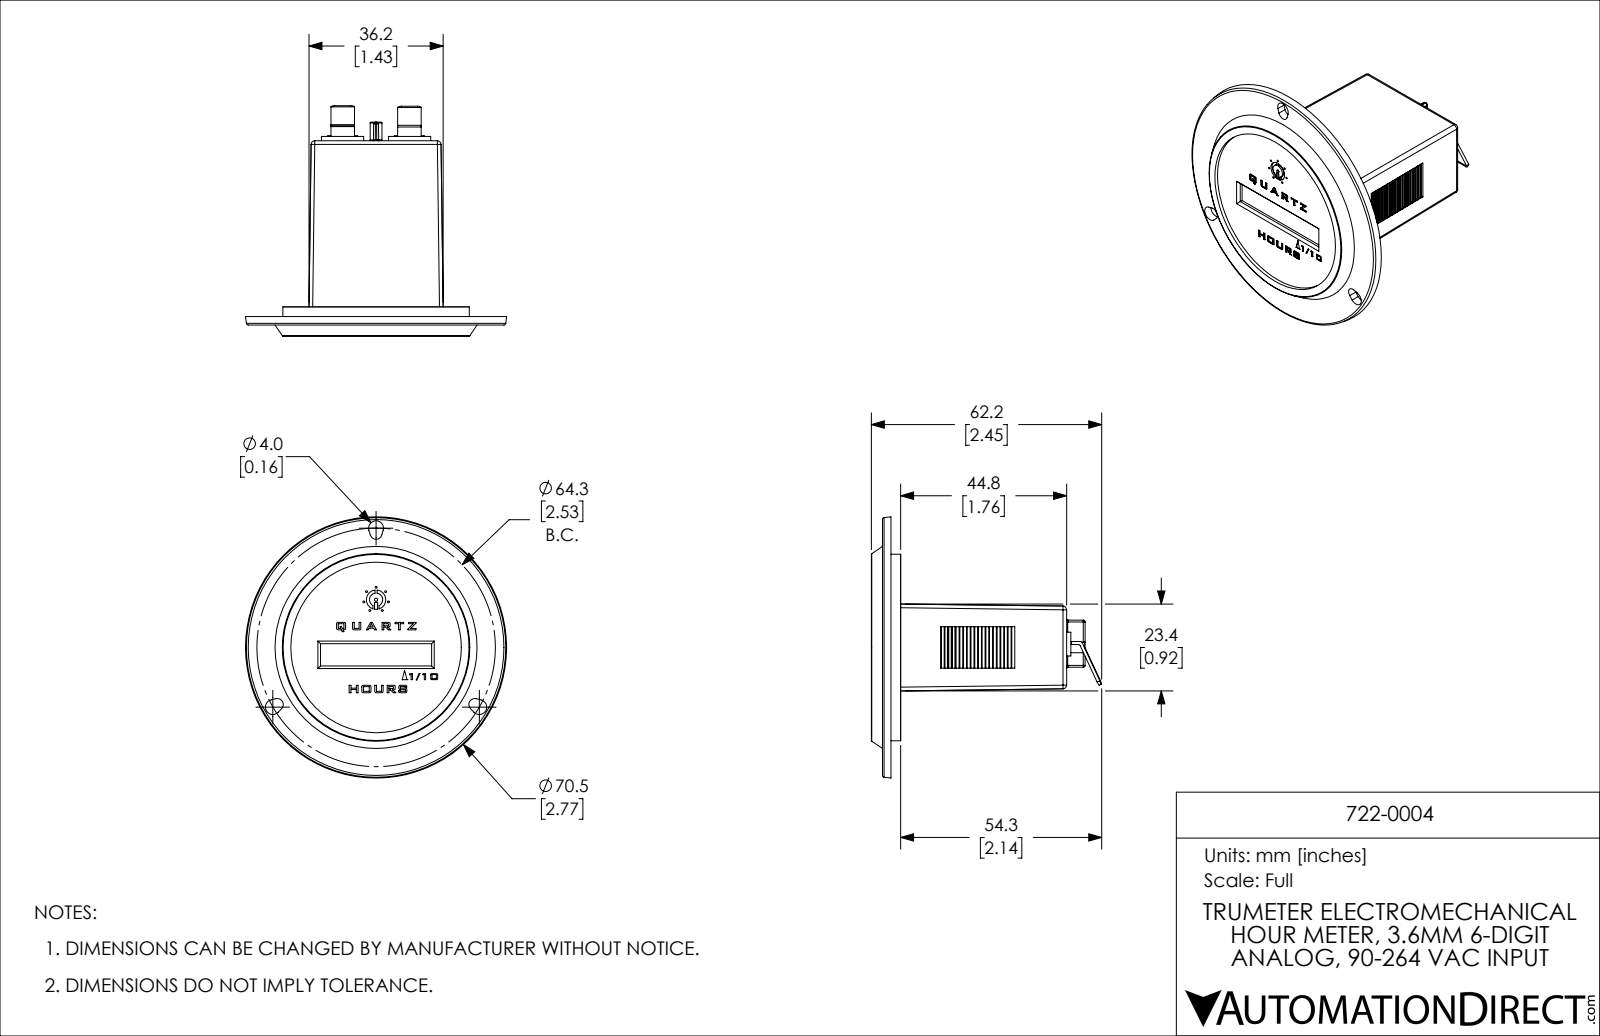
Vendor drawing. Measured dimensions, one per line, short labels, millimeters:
name: 722-0004
written by: SolidWorks 2021 (CONFIG_CONTROL_DESIGN)
unit: mm
bodies: 1 solid, 749 faces (557 planar, 138 cylindrical, 54 other)
size: 70.46 × 70.46 × 62.16
volume: 19 947 mm³; area: 24 460 mm²
holes: 7× ⌀0.5, 4× ⌀1.5, 1× ⌀0.84, 1× ⌀5.26, 1× ⌀46
bosses: 1× ⌀50.3, 1× ⌀3.58
rounds: 30× R0.5, 17× R1, 15× R0.3, 6× R1.5, 4× R0.35, 4× R1.75, 4× R2.5, 3× R1.6
face distances: 2, 2.9, 2.3, 4.3, 0.6, 1.4, 2.4, 3, 4.9, 1.9
hole spacings: 3.36, 2.85, 6.5, 5.16, 2.84, 3.37, 5.15, 5.51
